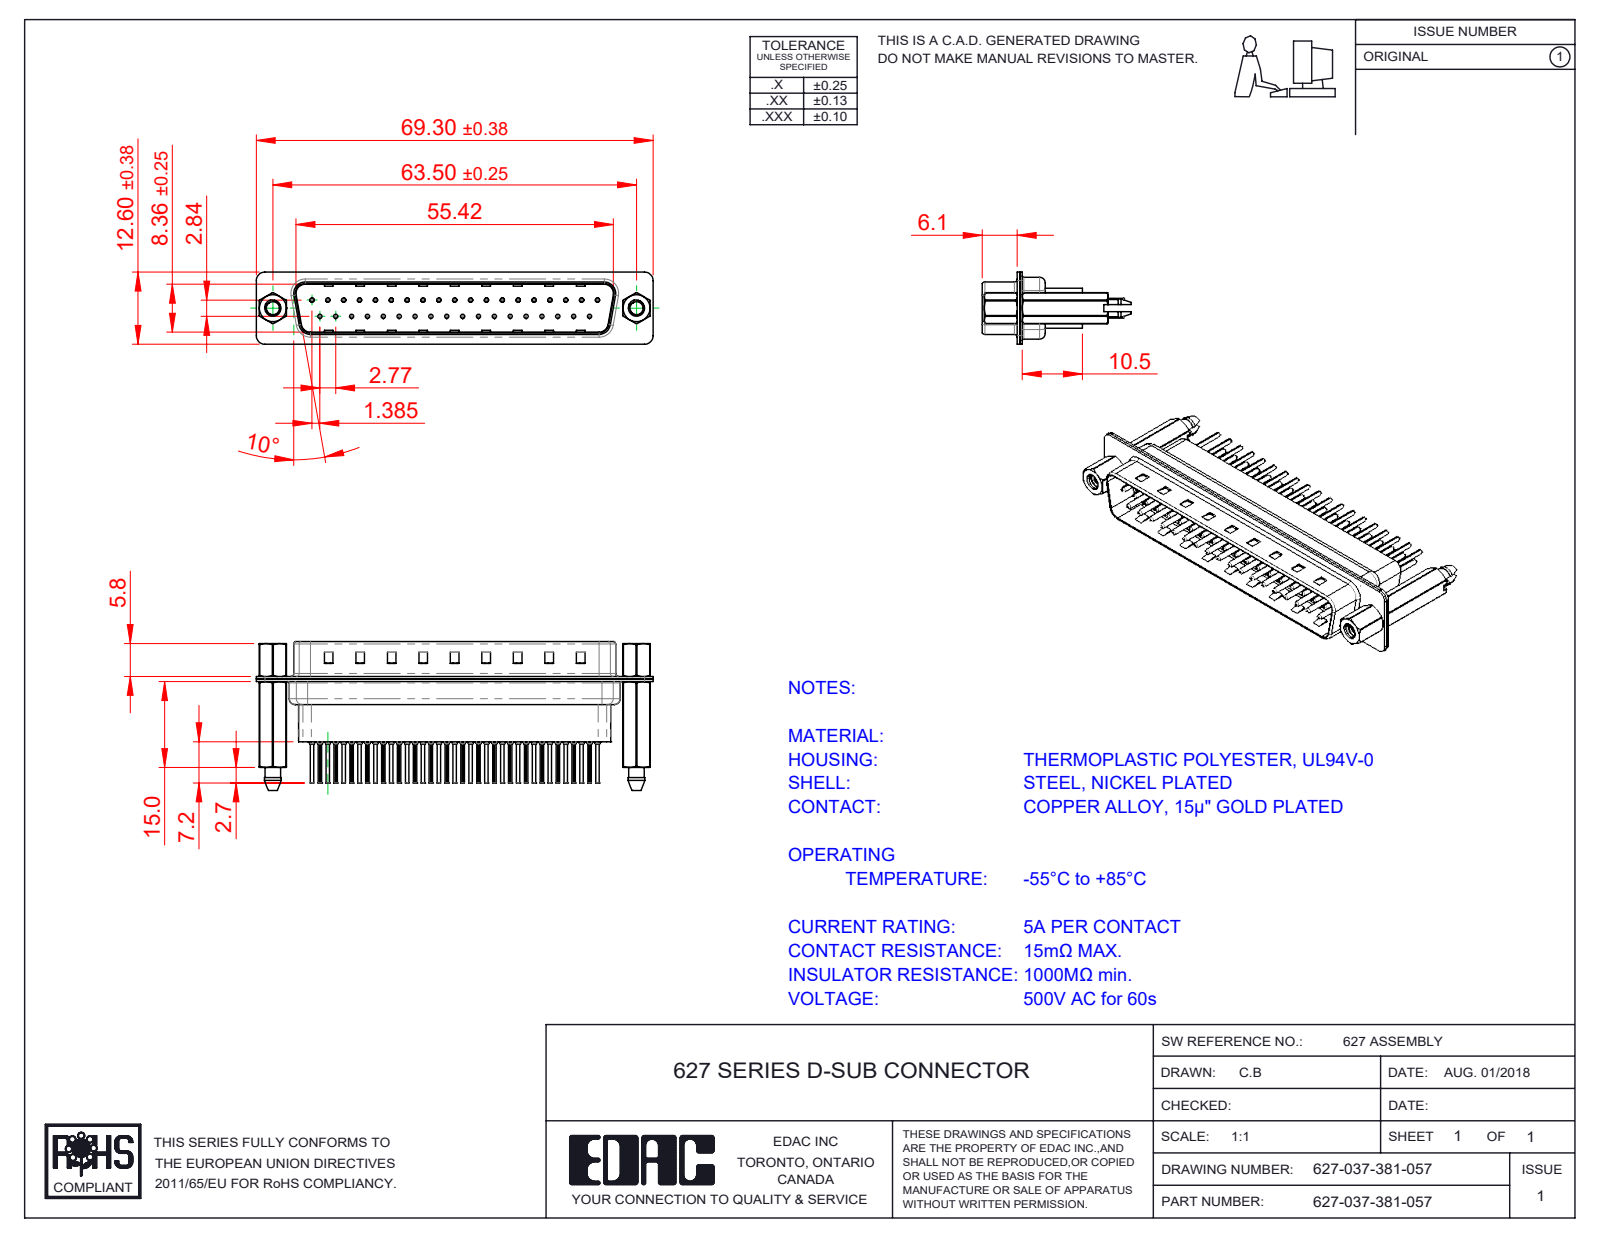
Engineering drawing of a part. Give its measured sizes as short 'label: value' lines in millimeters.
name: 627 4-40 Threaded Boardlock_HP81; 627 Shell Rear_37 Contacts; 627 4-40 Hex Standoff; 627-037-381-057 (+4 more)
written by: SolidWorks 2020 (CONFIG_CONTROL_DESIGN)
unit: mm
bodies: 44 solids, 4272 faces (1145 planar, 1648 cylindrical, 1479 other)
size: 69.3 × 25.9 × 12.6
volume: 5 936 mm³; area: 15 227 mm²
holes: 37× ⌀0.2, 37× ⌀0.35, 37× ⌀1.1, 37× ⌀1.6, 2× ⌀2.26, 2× ⌀2.29, 2× ⌀4, 2× ⌀4.8
bosses: 37× ⌀2, 37× ⌀1.5, 37× ⌀0.75, 37× ⌀0.6, 2× ⌀4.9, 2× ⌀2.79
rounds: 74× R0.1, 18× R1.5, 12× R2, 10× R1.6, 8× R0.5, 4× R0.25, 4× R0.6, 4× R0.65
face distances: 0.4, 0.82, 9.58, 0.45, 0.68, 7.68, 1.5, 1.08, 8.08, 8.76
hole spacings: 3.16, 2.77, 5.54, 8.31, 5.04, 10.1, 11.08, 12.78
